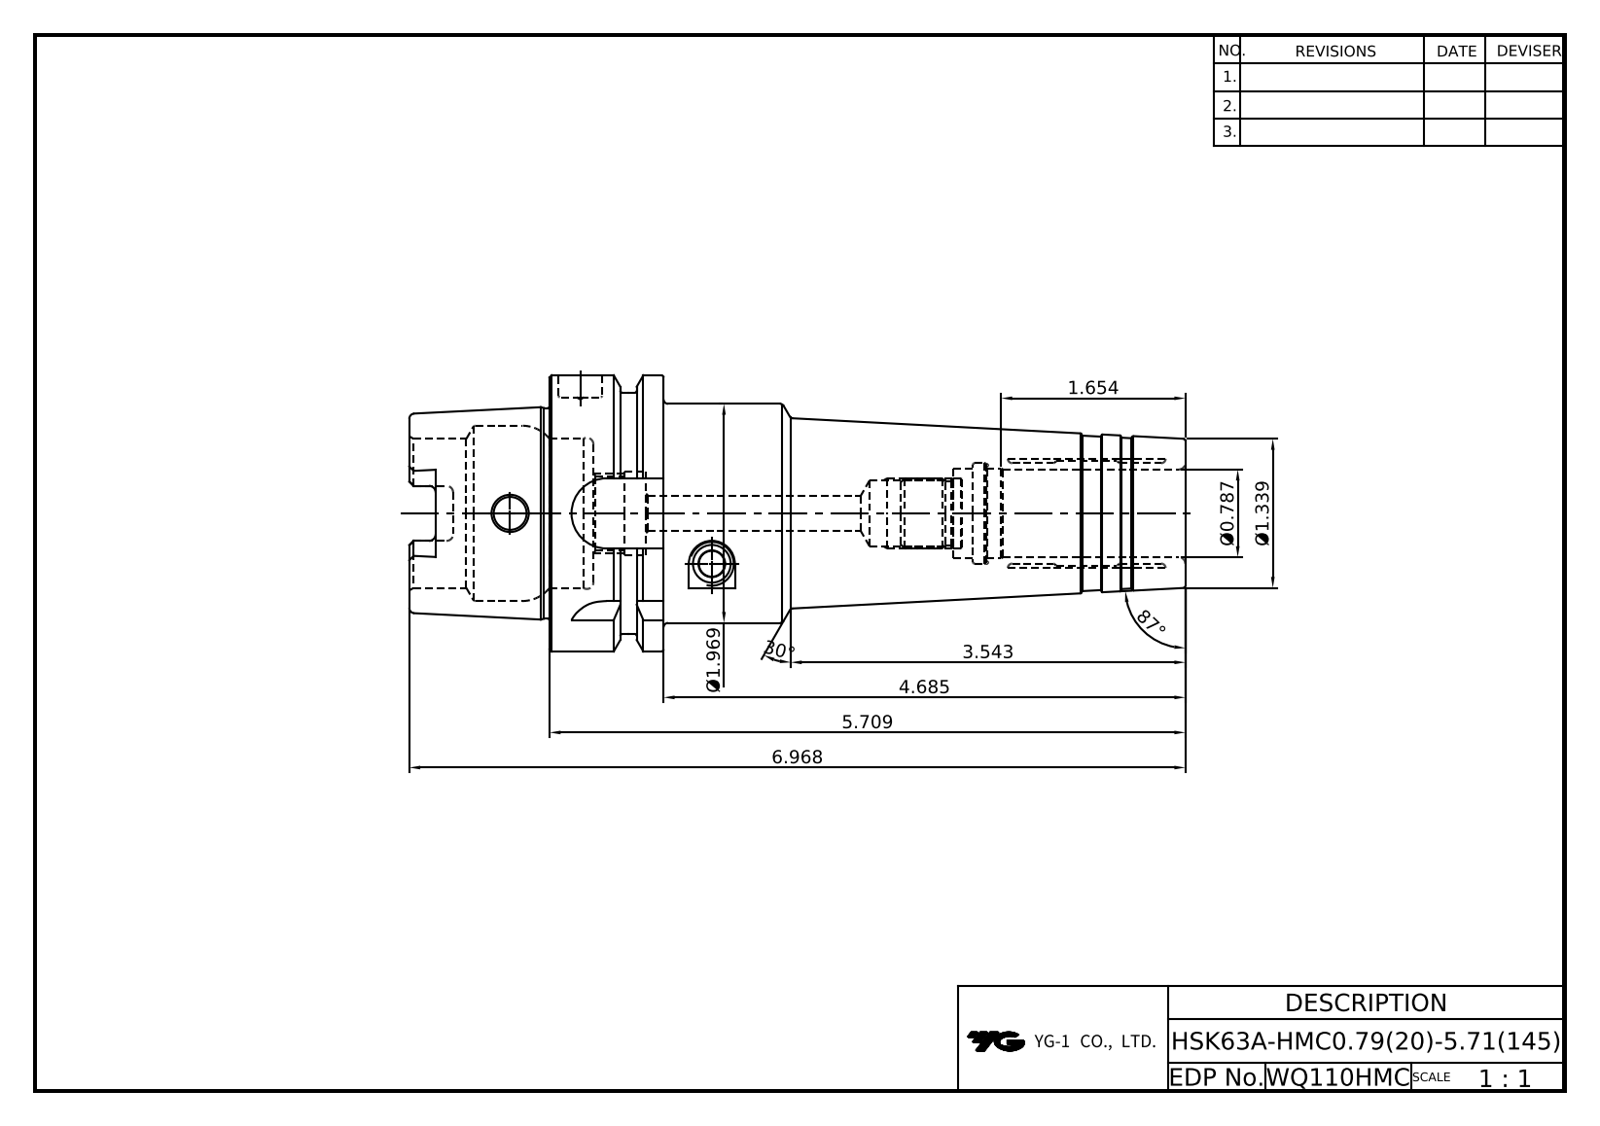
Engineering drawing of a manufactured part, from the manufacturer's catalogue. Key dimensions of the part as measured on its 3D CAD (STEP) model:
Part name (STEP PRODUCT): LO-HSK63A-HMC20-145
STEP written by: Autodesk Inventor 2020 (AUTOMOTIVE_DESIGN)
Units: millimetres
Bodies: 1 solid, 136 faces (42 planar, 34 cylindrical, 60 other)
Overall size (bounding box): 177 × 63 × 63
Volume: 221 597 mm³ · Surface area: 42 353 mm²
Round holes (diameter × count): ⌀7.5 ×1, ⌀8 ×1, ⌀10 ×1, ⌀14.92 ×1, ⌀16.92 ×1, ⌀19 ×1, ⌀20 ×1, ⌀20.4 ×1, ⌀34 ×1, ⌀40 ×1
Round bosses / shafts (diameter × count): ⌀63 ×1, ⌀55 ×1, ⌀50 ×1, ⌀48.04 ×1
Partial cylindrical surfaces — rounded edges, fillets, slot ends (radius × count): R1.5 ×6, R2.88 ×4, R8 ×4
Main face-to-face distances: 26, 10, 16, 145, 135, 119, 32, 53, 42, 58
